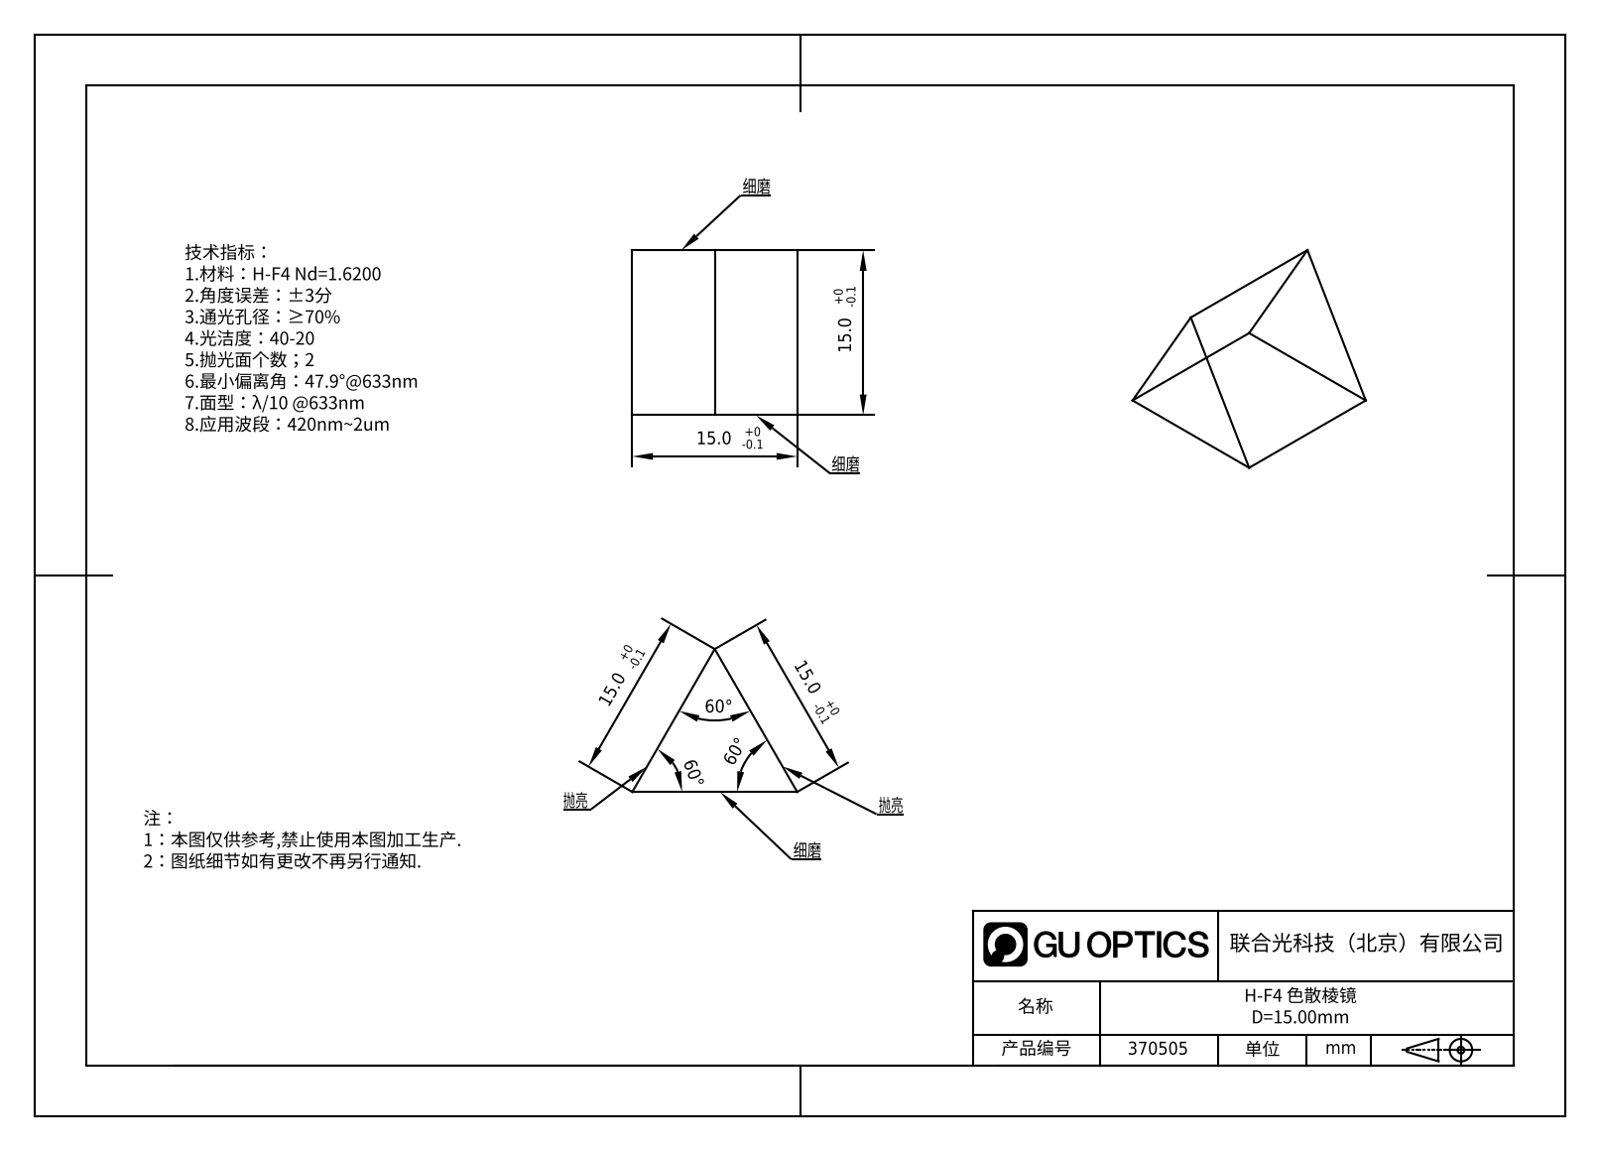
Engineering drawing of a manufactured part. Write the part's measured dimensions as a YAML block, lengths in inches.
part_name: "GPD-015-A2"
step_written_by: "SolidWorks 2022 (AUTOMOTIVE_DESIGN)"
units: inches
bodies: {solids: 1, faces: 20, planar: 20, cylindrical: 0, other: 0}
overall_size: [0.591, 0.587, 0.509]
volume: 0.089
surface_area: 1.33
face_to_face_distances: [0.591]
